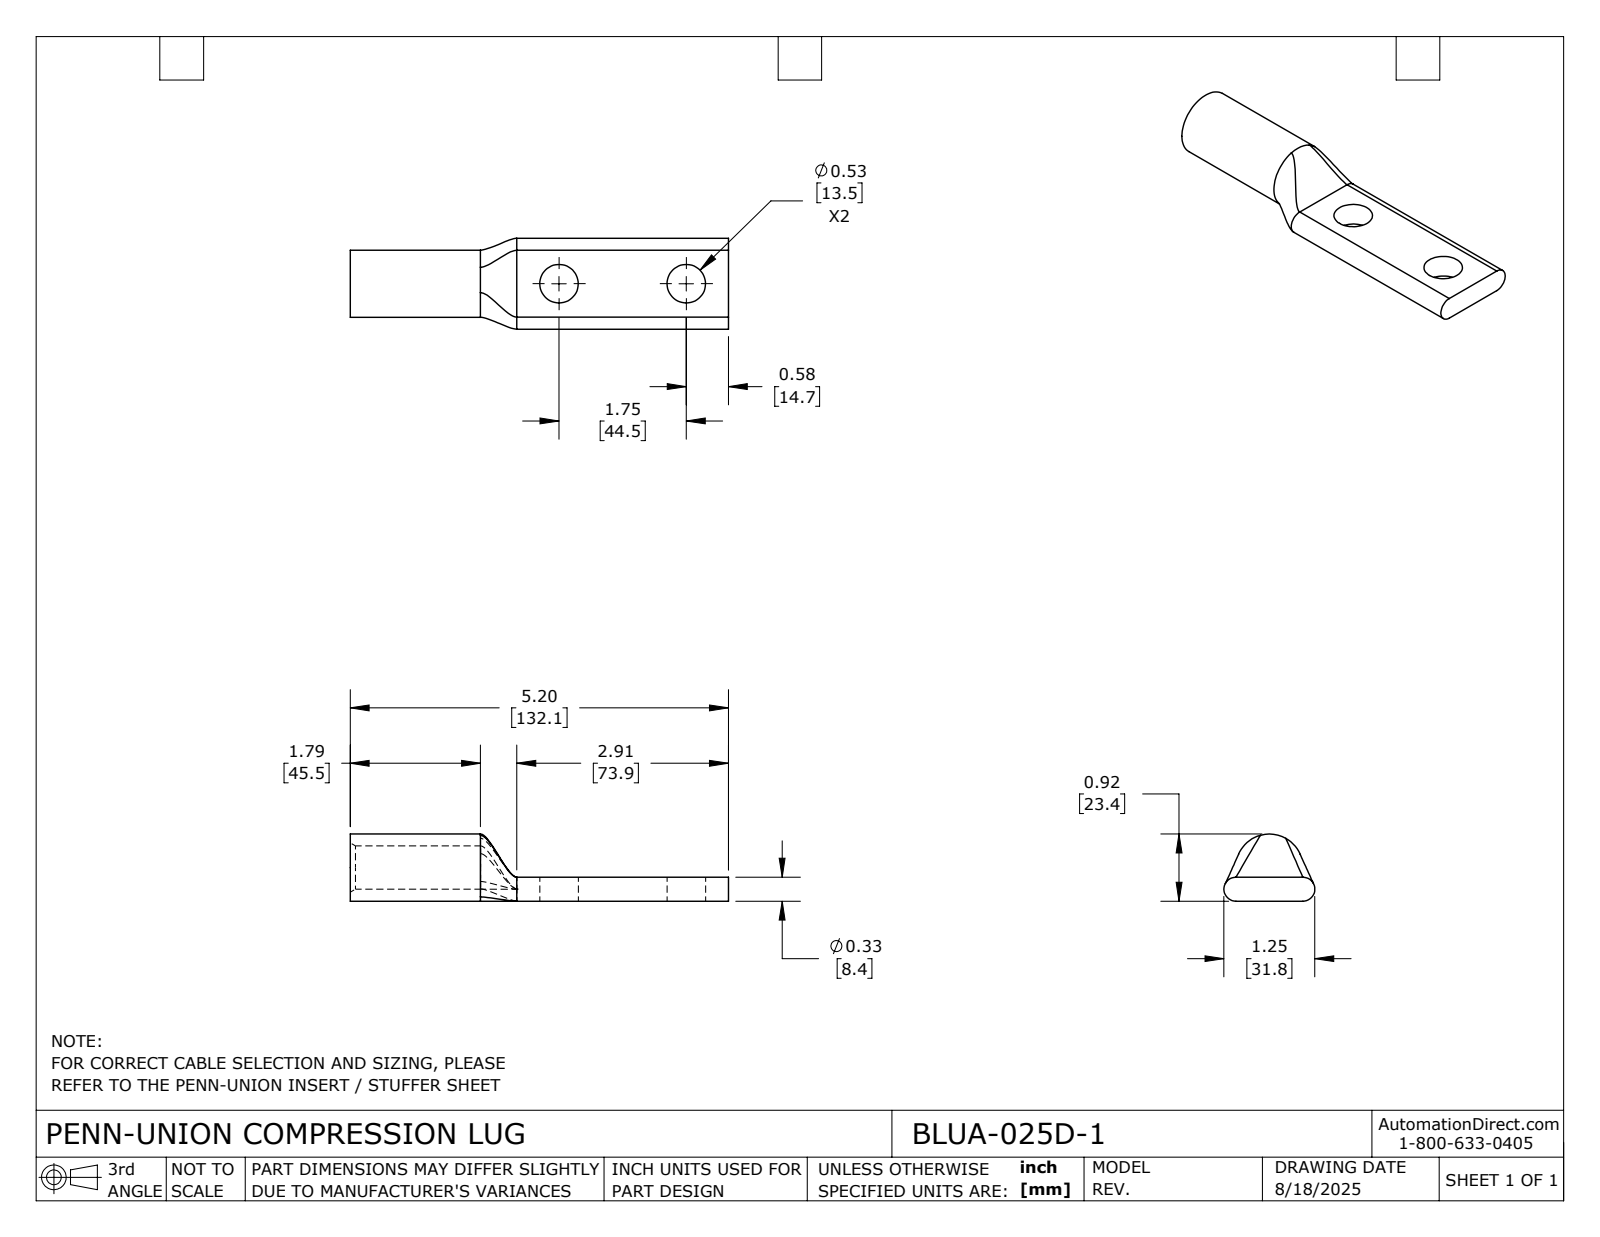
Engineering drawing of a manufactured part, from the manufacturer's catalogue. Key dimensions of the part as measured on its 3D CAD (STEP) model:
Part name (STEP PRODUCT): BLUA-025D-1
STEP written by: SolidWorks 2024 (CONFIG_CONTROL_DESIGN)
Units: inches
Bodies: 1 solid, 26 faces (5 planar, 11 cylindrical, 10 other)
Overall size (bounding box): 5.2 × 1.25 × 0.923
Volume: 1.877 in³ · Surface area: 20.65 in²
Round holes (diameter × count): ⌀0.53 ×2, ⌀0.595 ×1
Round bosses / shafts (diameter × count): ⌀0.923 ×1
Partial cylindrical surfaces — rounded edges, fillets, slot ends (radius × count): R0.165 ×2
Main face-to-face distances: 0.33, 5.2, 2.29, 2.91
Hole centre spacings: 1.75
